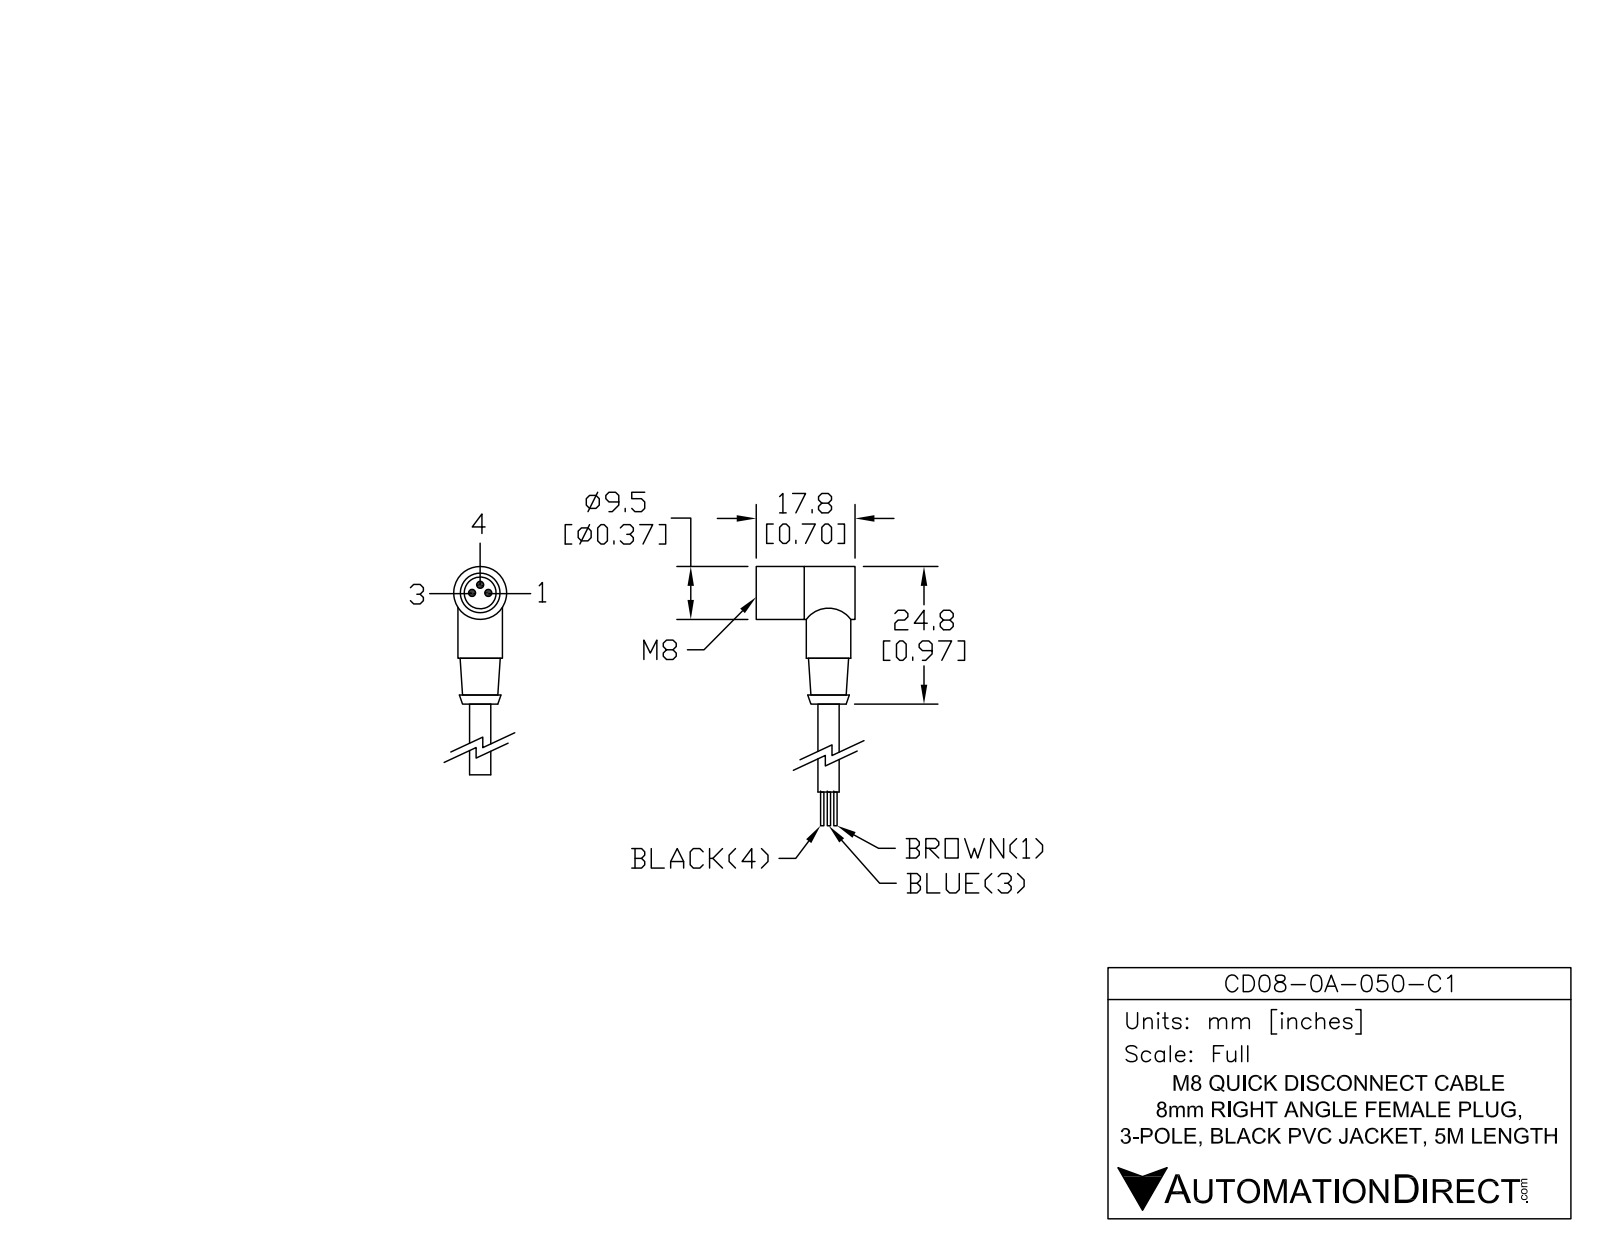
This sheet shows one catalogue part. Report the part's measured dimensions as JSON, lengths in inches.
{"part_name": "CD08-0A-050-C1", "step_written_by": "SolidWorks 2017 (AUTOMOTIVE_DESIGN)", "units": "inches", "bodies": {"solids": 4, "faces": 307, "planar": 222, "cylindrical": 82, "other": 3}, "overall_size": [5.063, 0.752, 0.394], "volume_in3": 0.261, "surface_area_in2": 5.112, "round_holes": [[0.035, 3], [0.22, 1], [0.315, 1]], "round_bosses_or_shafts": [[0.394, 2], [0.26, 1], [0.217, 1], [0.189, 1]], "partial_cylinders_radius": [[0.02, 1], [0.193, 1]], "face_to_face_distances": [0.354, 0.024, 0.181, 0.122, 0.157, 0.28, 0.303, 3.937, 0.098, 0.205], "hole_center_spacings": [0.063, 0.089, 0.126]}
